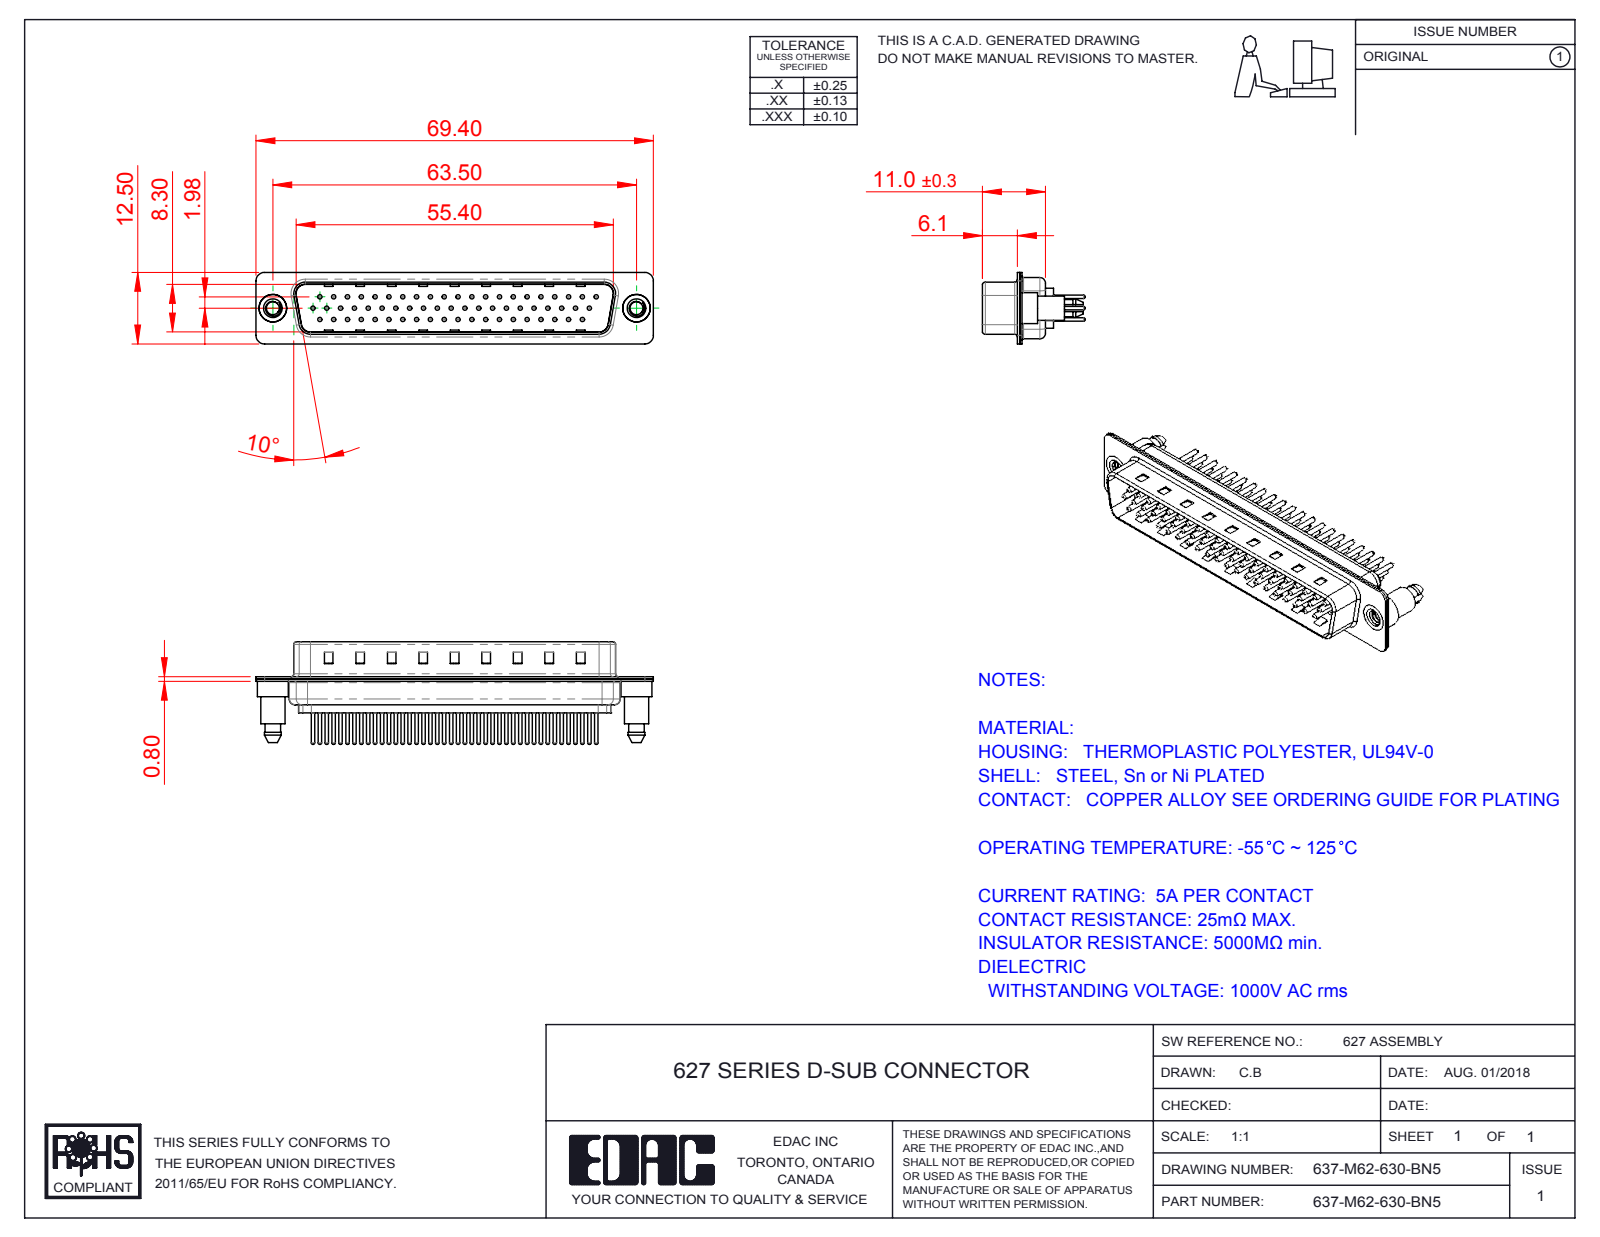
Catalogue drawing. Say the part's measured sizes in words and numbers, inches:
The part is named "637M Shell Rear_62 Contacts; 637M Housing_62 Contacts; 637M Shell Front_62 Contacts; 637M Contact Row 1_30 (+4 more)". Its 3-D file was written by "SolidWorks 2016 (CONFIG_CONTROL_DESIGN)". It is 67 solids with 2756 faces: 653 planar, 1041 cylindrical and 1062 other. Overall it measures 2.732 by 0.705 by 0.492 inches. Its volume is 0.247 cubic inches and its surface area 18.21 square inches. Round holes: 62 of diameter 0.03, 62 of diameter 0.063, 62 of diameter 0.079, 2 of diameter 0.089, 2 of diameter 0.157, 2 of diameter 0.189. Round bosses or shafts: 62 of diameter 0.059, 62 of diameter 0.024, 2 of diameter 0.213, 2 of diameter 0.193, 2 of diameter 0.167. Partial cylindrical surfaces (rounded edges, fillets, slot ends): 18 of radius 0.059, 12 of radius 0.079, 10 of radius 0.063, 8 of radius 0.02, 4 of radius 0.01, 4 of radius 0.024, 4 of radius 0.026, 4 of radius 0.035. The main face-to-face distances are 0.016, 0.031, 0.374, 0.358, 0.343, 0.39, 0.03, 0.014, 0.232, 0.047. The hole center spacings are 0.285, 0.091, 0.095, 0.163, 0.38, 0.19, 0.57, 0.435.
